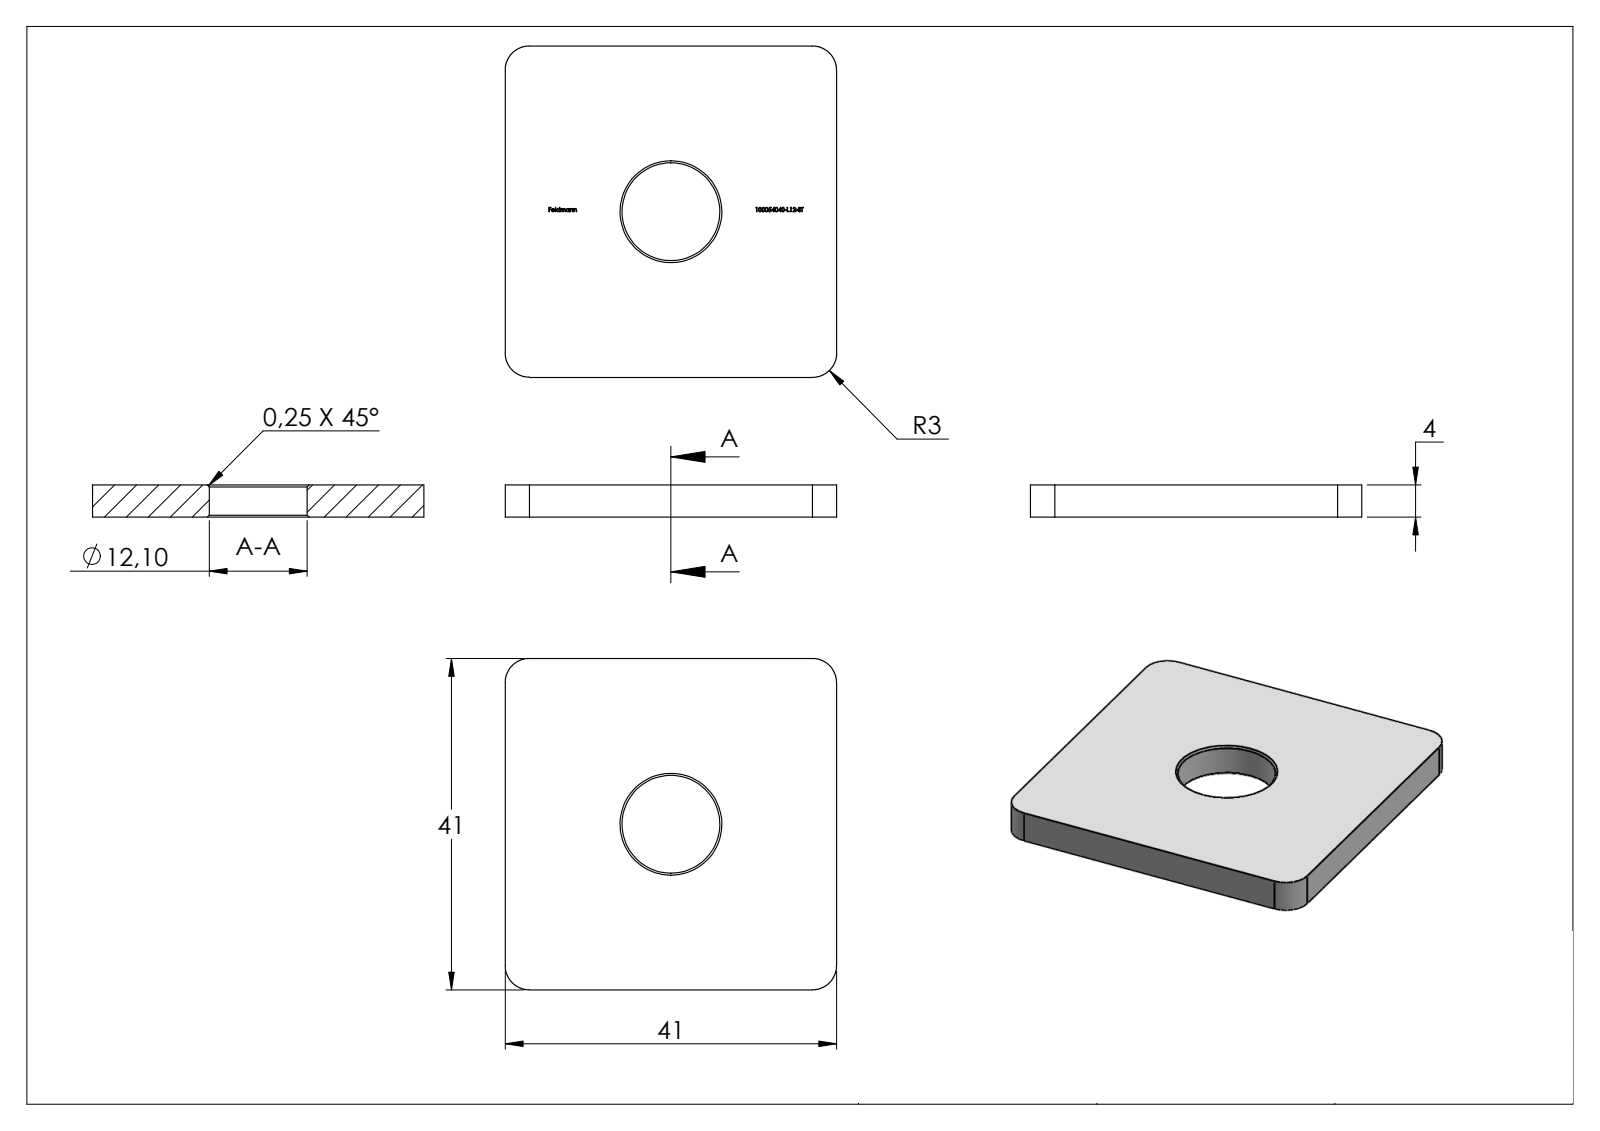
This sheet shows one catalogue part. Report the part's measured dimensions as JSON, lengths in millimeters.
{"part_name": "100054040-L12-ST", "step_written_by": "SolidWorks 2018 (CONFIG_CONTROL_DESIGN)", "units": "millimeters", "bodies": {"solids": 1, "faces": 297, "planar": 168, "cylindrical": 5, "other": 124}, "overall_size": [41, 41, 4], "volume_mm3": 6231, "surface_area_mm2": 3898, "round_holes": [[12.1, 1]], "partial_cylinders_radius": [[3, 4]], "face_to_face_distances": [4, 41, 3.9, 20.5, 0.35, 28.65, 5.61, 0.81, 20.68, 20.32]}
